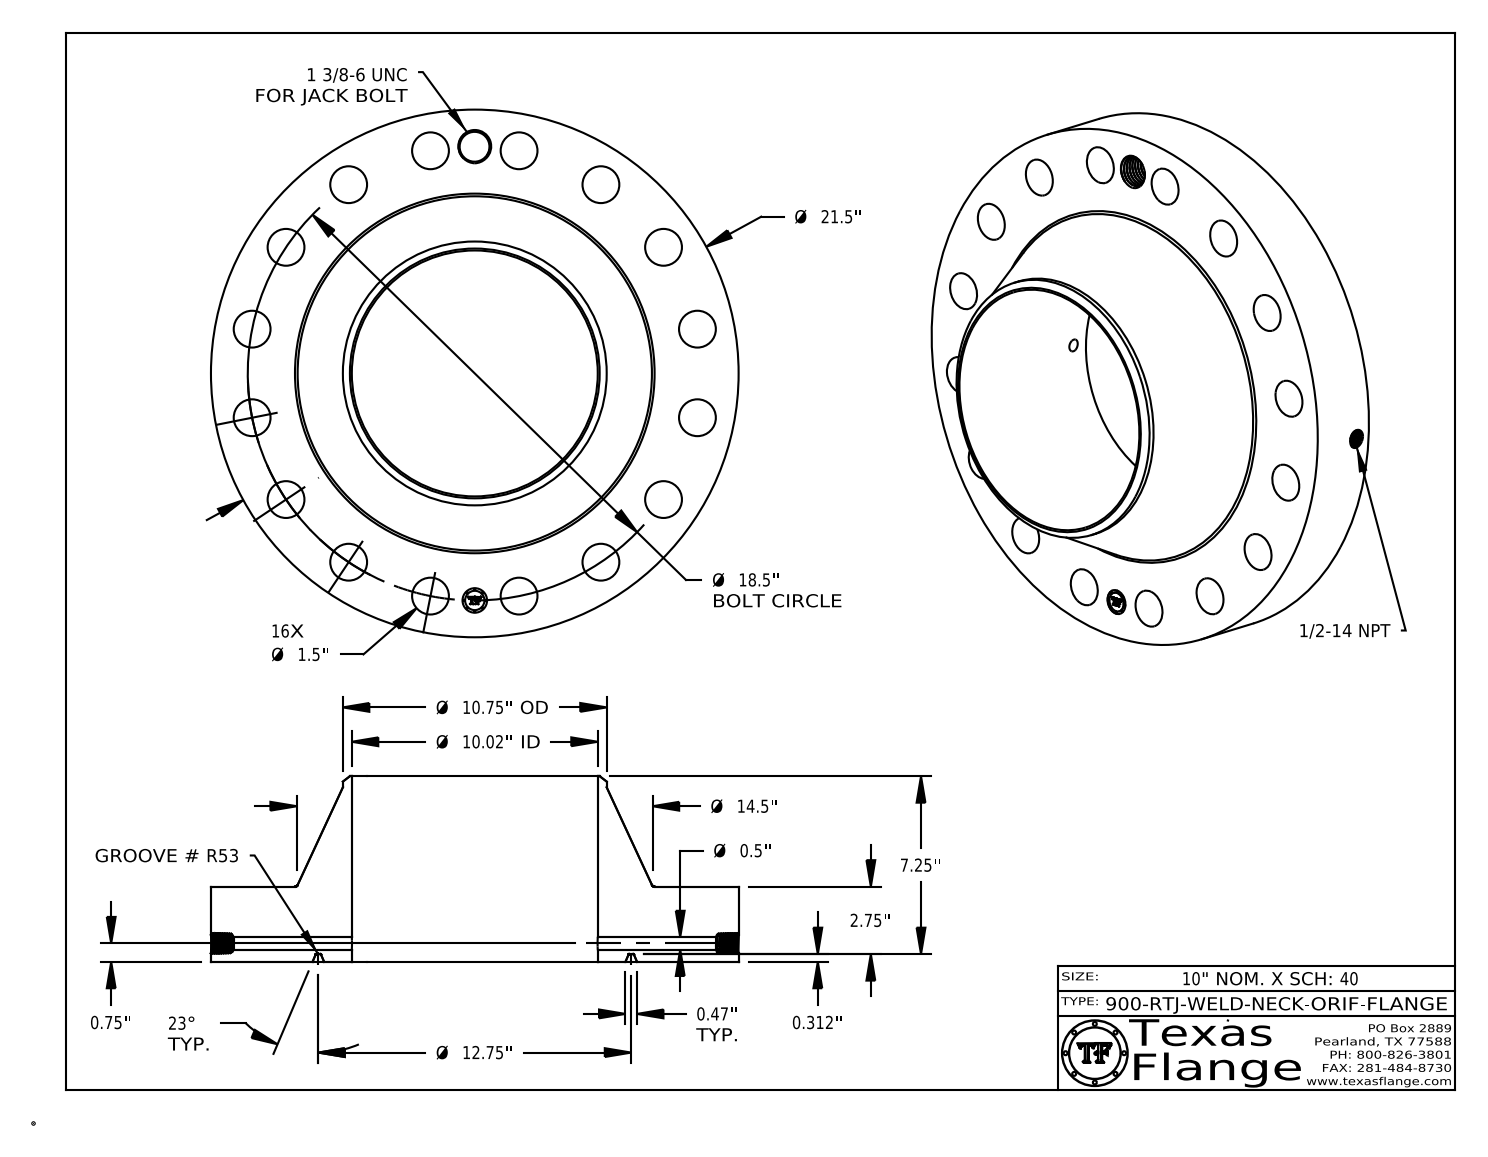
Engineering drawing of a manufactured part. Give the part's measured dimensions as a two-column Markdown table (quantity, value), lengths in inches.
| quantity | value |
| --- | --- |
| part name | 900-RTJ-WELD-NECK |
| STEP written by | CATIA V5 STEP AP214 (AUTOMOTIVE_DESIGN) |
| units | inches |
| bodies | 1 solid, 813 faces (370 planar, 114 cylindrical, 329 other) |
| overall size | 21.5 × 21.5 × 7.562 |
| volume | 968.2 in³ |
| surface area | 1 352 in² |
| round holes (diameter × count) | 1.5 × 16, 0.5 × 1, 0.672 × 1, 1 × 1, 1.219 × 1, 10.02 × 1 |
| round bosses / shafts (diameter × count) | 0.061 × 8, 21.5 × 1, 10.75 × 1, 0.788 × 1 |
| main face-to-face distances | 3.062, 0.312, 2.75, 7.562, 7.25, 4.5, 3.047, 2.735, 0.015, 4.515 |
| hole center spacings | 10.278, 17.092, 3.609, 9.25, 7.08, 7.08, 9.25, 13.081 |
